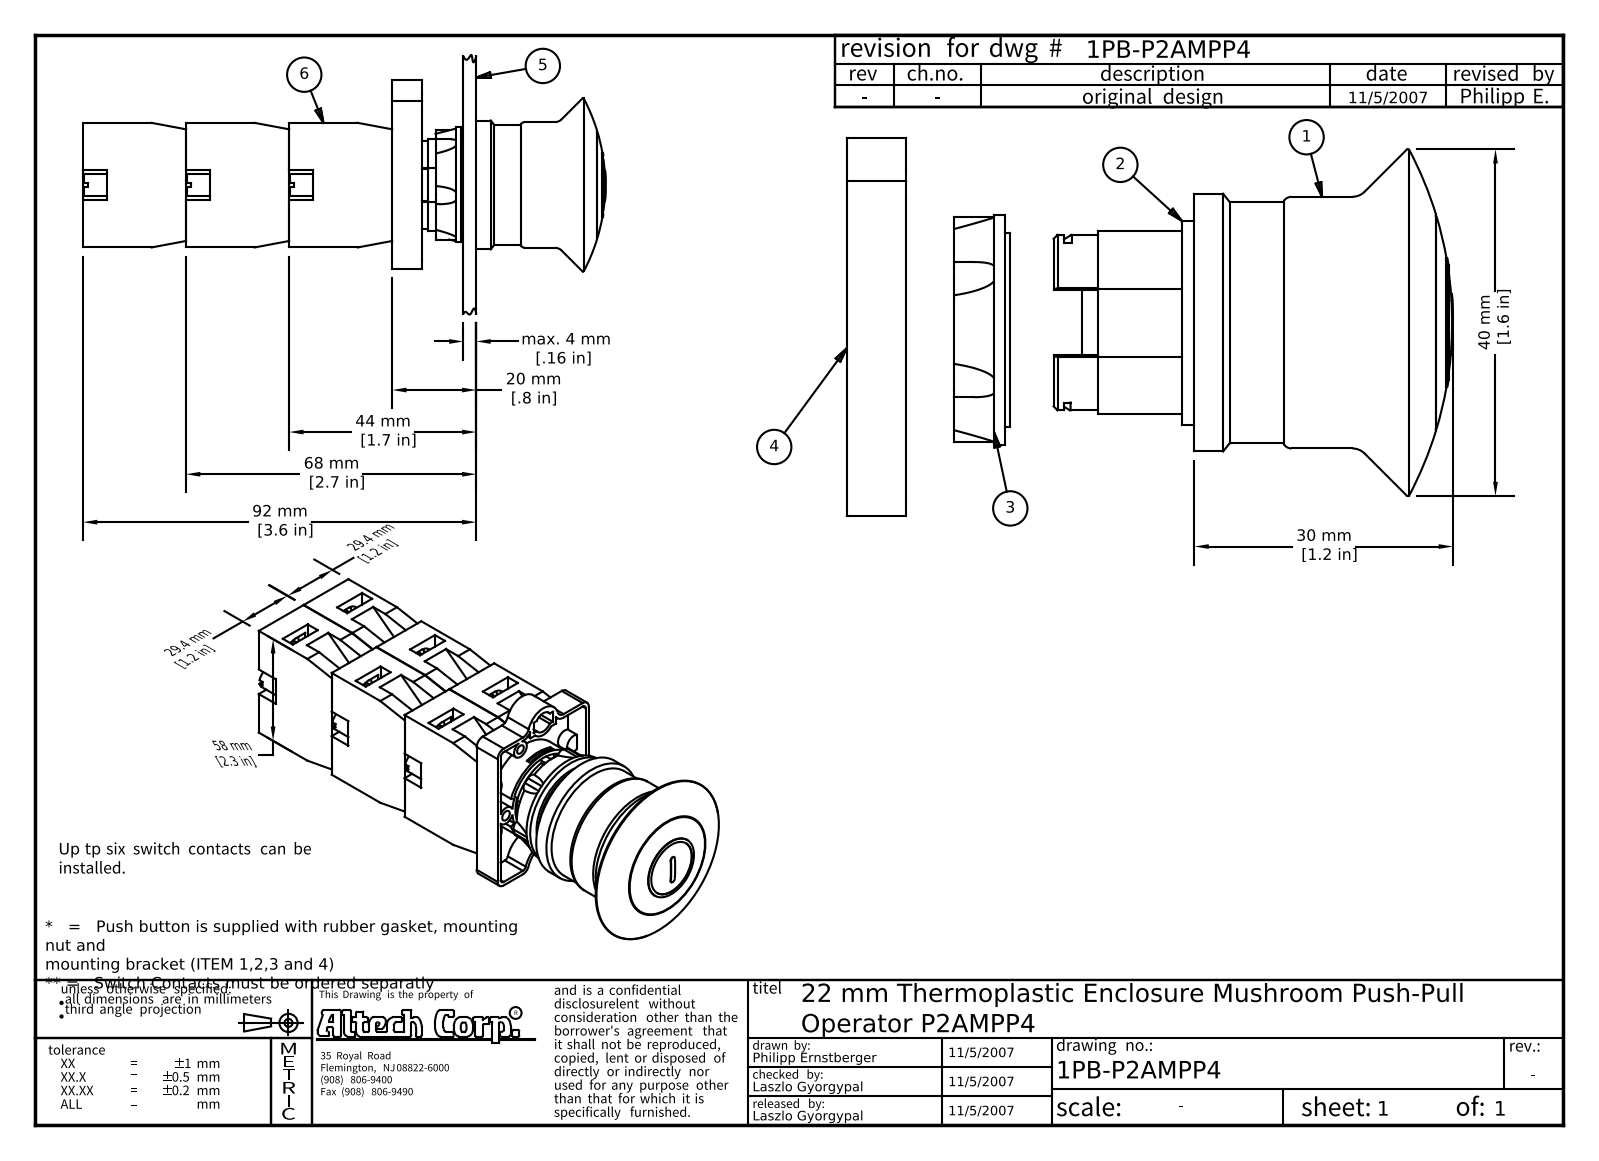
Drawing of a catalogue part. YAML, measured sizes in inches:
part_name: "P2AMPP4_assembly; P2AMPP4_operator; P2AMPP4; 2PRG1 (+7 more)"
step_written_by: "Autodesk Inventor 2008 (AUTOMOTIVE_DESIGN)"
units: inches
bodies: {solids: 29, faces: 1171, planar: 629, cylindrical: 201, other: 341}
overall_size: [4.791, 2.38, 1.772]
volume: 5.378
surface_area: 72.62
round_holes:
  - {diameter: 0.098, count: 6}
  - {diameter: 0.087, count: 2}
  - {diameter: 0.102, count: 2}
  - {diameter: 0.528, count: 1}
  - {diameter: 0.693, count: 1}
  - {diameter: 0.819, count: 1}
  - {diameter: 0.886, count: 1}
  - {diameter: 1.114, count: 1}
round_bosses_or_shafts:
  - {diameter: 0.118, count: 6}
  - {diameter: 0.108, count: 4}
  - {diameter: 0.059, count: 4}
  - {diameter: 0.197, count: 2}
  - {diameter: 0.165, count: 2}
  - {diameter: 1.181, count: 1}
  - {diameter: 1.154, count: 1}
  - {diameter: 1.106, count: 1}
partial_cylinders:
  - {radius: 0.039, count: 15}
  - {radius: 0.059, count: 12}
  - {radius: 0.079, count: 8}
  - {radius: 0.089, count: 6}
  - {radius: 0.026, count: 2}
  - {radius: 0.118, count: 2}
  - {radius: 0.13, count: 2}
  - {radius: 0.197, count: 2}
face_to_face_distances: [0.583, 0.579, 0.945, 0.118, 1.89, 1.161, 0.772, 1.142, 0.654, 2.543]
hole_center_spacings: [0.257, 1.026, 0.449, 0.482, 0.512, 0.571, 0.573, 0.676]
